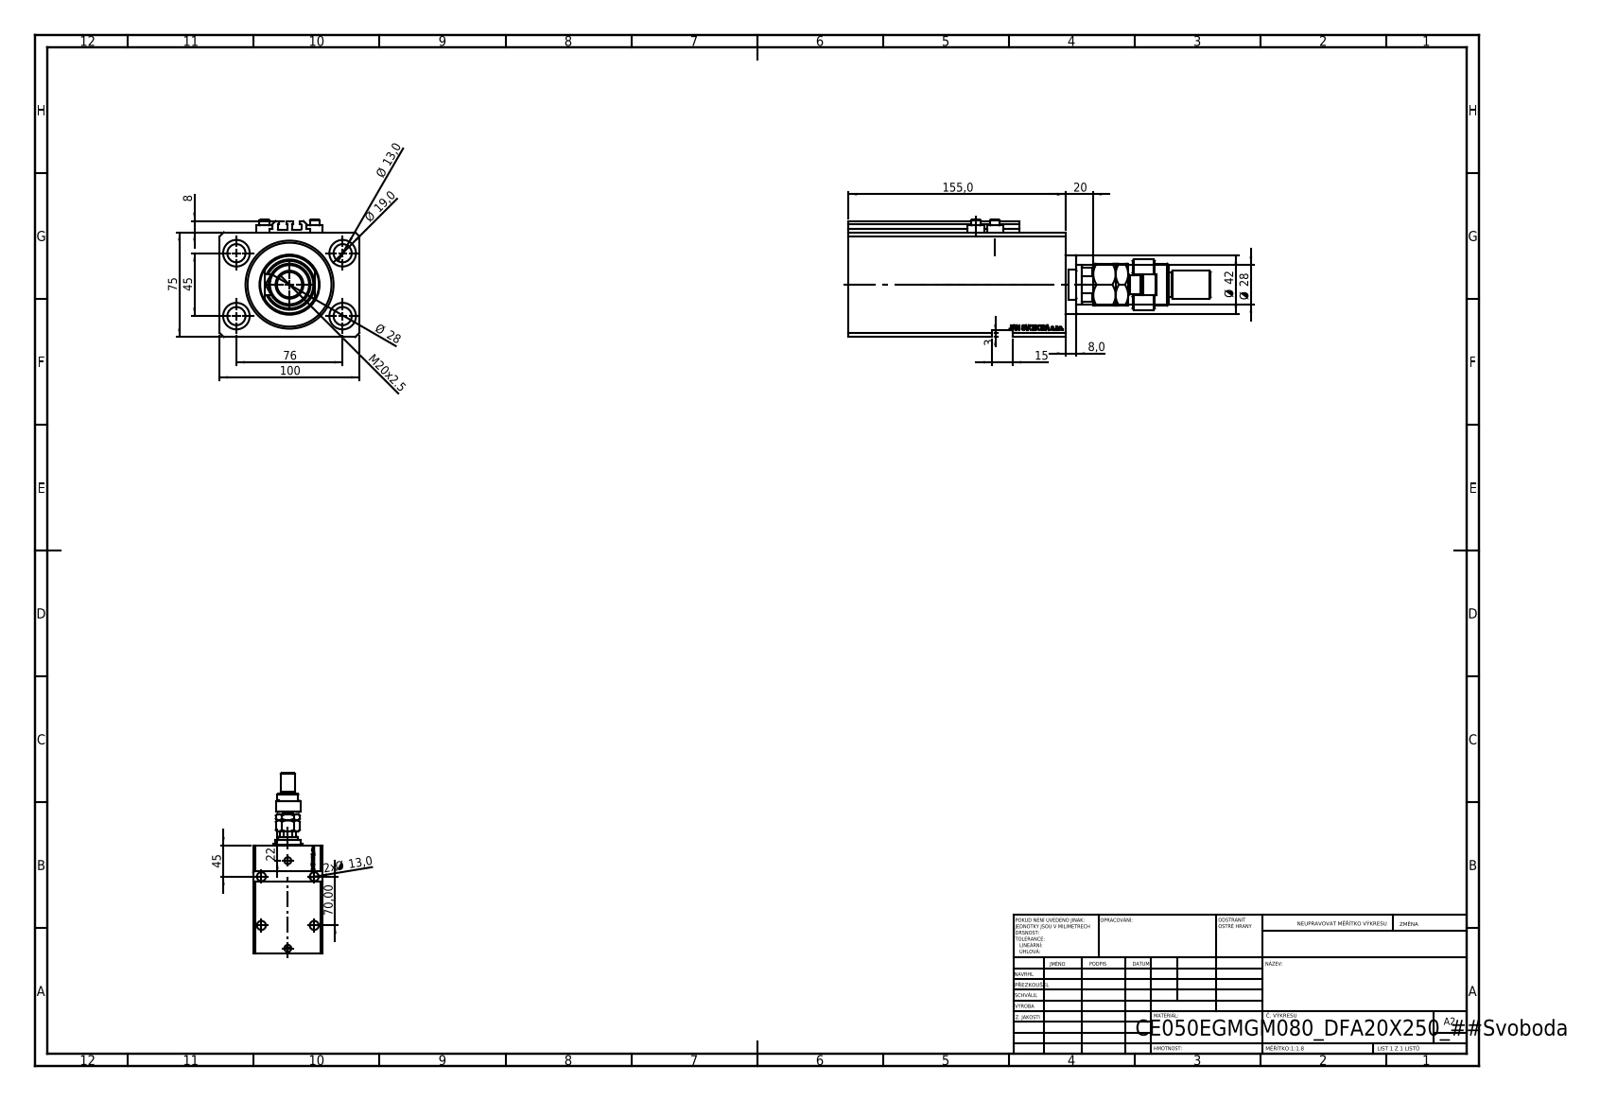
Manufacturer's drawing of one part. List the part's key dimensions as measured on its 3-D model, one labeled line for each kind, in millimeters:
Part name (STEP PRODUCT): V250CE_E_Body; MFA; V250CE_VC_E; V250CE_C_VCP (+2 more)
STEP written by: SolidWorks 2019 (CONFIG_CONTROL_DESIGN)
Units: millimetres
Bodies: 10 solids, 1193 faces (563 planar, 159 cylindrical, 471 other)
Overall size (bounding box): 259 × 100 × 84
Volume: 989 616 mm³ · Surface area: 189 158 mm²
Round holes (diameter × count): ⌀13 ×8, ⌀1.25 ×4, ⌀4 ×4, ⌀19 ×4, ⌀10 ×2, ⌀13.16 ×2, ⌀20 ×2, ⌀18.5 ×1, ⌀28 ×1, ⌀50 ×1, ⌀63 ×1
Round bosses / shafts (diameter × count): ⌀11.6 ×4, ⌀7 ×4, ⌀42 ×1, ⌀36 ×1, ⌀30 ×1, ⌀22 ×1, ⌀20 ×1, ⌀18 ×1
Partial cylindrical surfaces — rounded edges, fillets, slot ends (radius × count): R0.2 ×10, R7.5 ×1, R12 ×1, R13.5 ×1
Main face-to-face distances: 75, 100, 20, 155, 11.9, 143.1, 135, 123.1, 10, 55
Hole centre spacings: 44.16, 76, 13.6, 20.72, 27.59, 33.62, 36, 38.48
